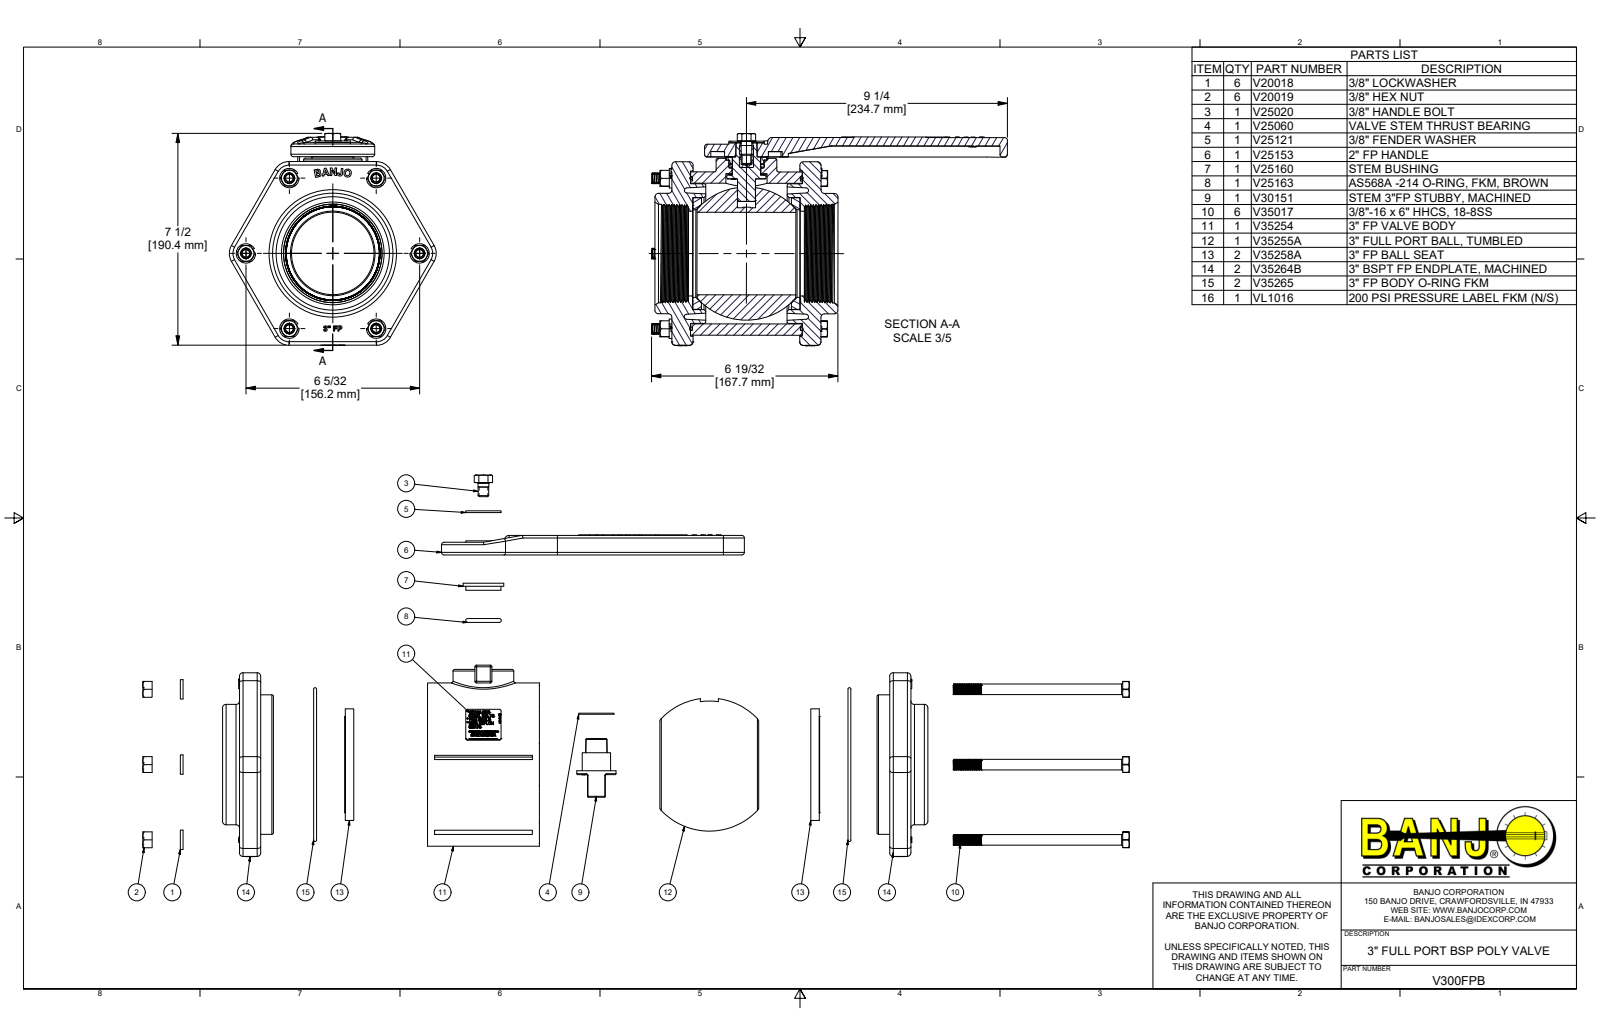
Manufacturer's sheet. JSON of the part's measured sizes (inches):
{"part_name": "V300FPB; V35254; VL1000; V35264B (+8 more)", "step_written_by": "Autodesk Inventor 2019 (AUTOMOTIVE_DESIGN)", "units": "inches", "bodies": {"solids": 43, "faces": 4973, "planar": 2777, "cylindrical": 542, "other": 1654}, "overall_size": [106.072, 7.502, 7.331], "volume_in3": 116.8, "surface_area_in2": 5555, "round_holes": [[0.171, 12], [0.282, 6], [0.307, 6], [0.385, 6], [0.44, 6], [0.375, 3], [0.307, 1], [0.406, 1], [0.681, 1], [0.962, 1], [1, 1], [1.016, 1]], "round_bosses_or_shafts": [[0.687, 6], [0.375, 6], [5.78, 1], [5.138, 1], [4.94, 1], [4.26, 1], [3.95, 1], [3.412, 1]], "partial_cylinders_radius": [[0.06, 24], [0.125, 24], [0.032, 10], [0.09, 8], [0.32, 6], [0.562, 6], [0.059, 2], [0.084, 2]], "face_to_face_distances": [0.66, 4.62, 5.28, 0.75, 4.53, 0.09, 3.87, 0.735, 4.545, 0.075], "hole_center_spacings": [2.264, 2.805, 0.813, 3.075, 4.667, 5.418, 5.433, 1.452]}
